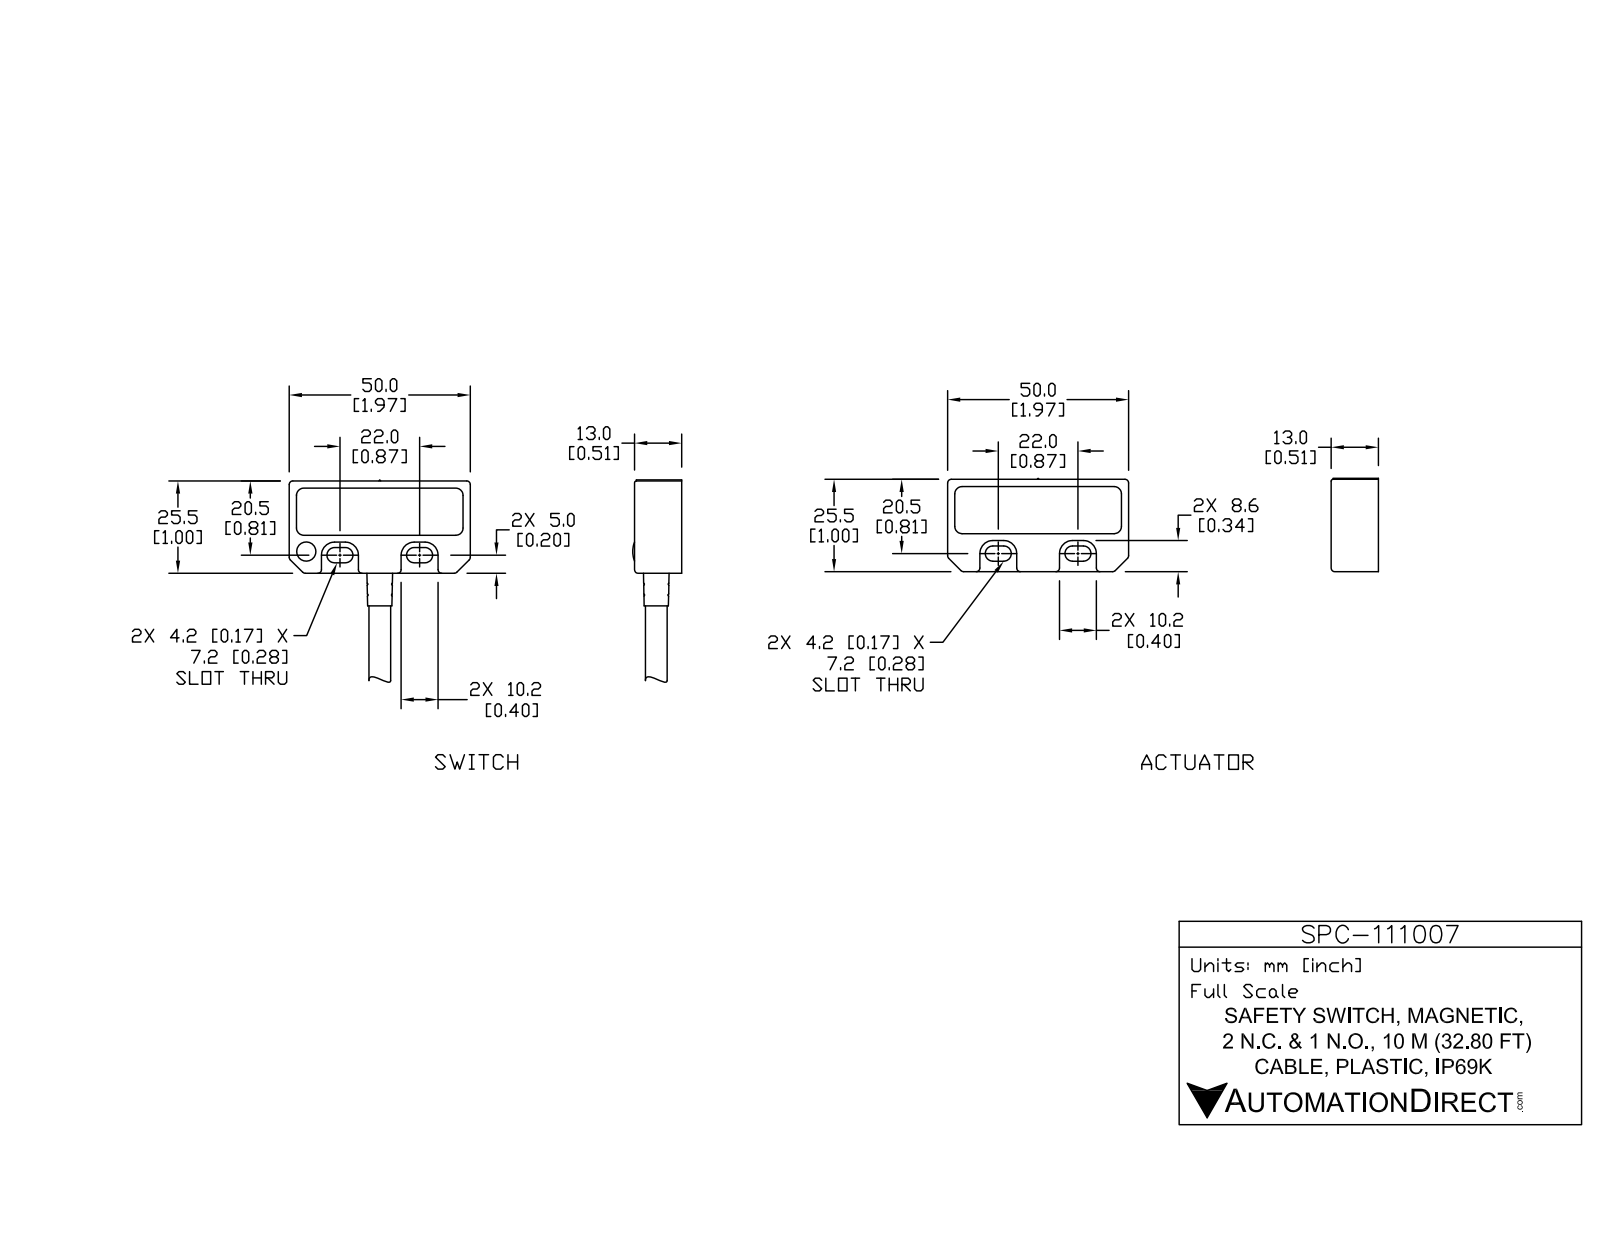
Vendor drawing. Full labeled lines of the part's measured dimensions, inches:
Part name (STEP PRODUCT): SPC-111007_2; SPC-111007_1; SPC-111007
STEP written by: SolidWorks 2017 (AUTOMOTIVE_DESIGN)
Units: inches
Bodies: 12 solids, 1147 faces (475 planar, 358 cylindrical, 314 other)
Overall size (bounding box): 8.091 × 1.969 × 0.543
Volume: 1.105 in³ · Surface area: 36.31 in²
Round holes (diameter × count): ⌀0.197 ×4, ⌀0.119 ×1, ⌀0.173 ×1, ⌀0.213 ×1, ⌀0.232 ×1, ⌀0.276 ×1
Round bosses / shafts (diameter × count): ⌀0.079 ×4, ⌀0.193 ×2, ⌀0.031 ×2, ⌀0.339 ×1, ⌀0.299 ×1, ⌀0.28 ×1, ⌀0.236 ×1, ⌀0.209 ×1
Partial cylindrical surfaces — rounded edges, fillets, slot ends (radius × count): R0.02 ×132, R0.039 ×36, R0.079 ×8, R0.083 ×8, R0.142 ×8, R0.181 ×8, R0.012 ×6, R0.14 ×4
Main face-to-face distances: 0.059, 0.457, 0.398, 0.047, 0.445, 0.504, 1.043, 0.098, 0.945, 1.909
Hole centre spacings: 0.221, 0.862, 1.062, 1.065, 1.283, 1.492, 1.55, 1.559
